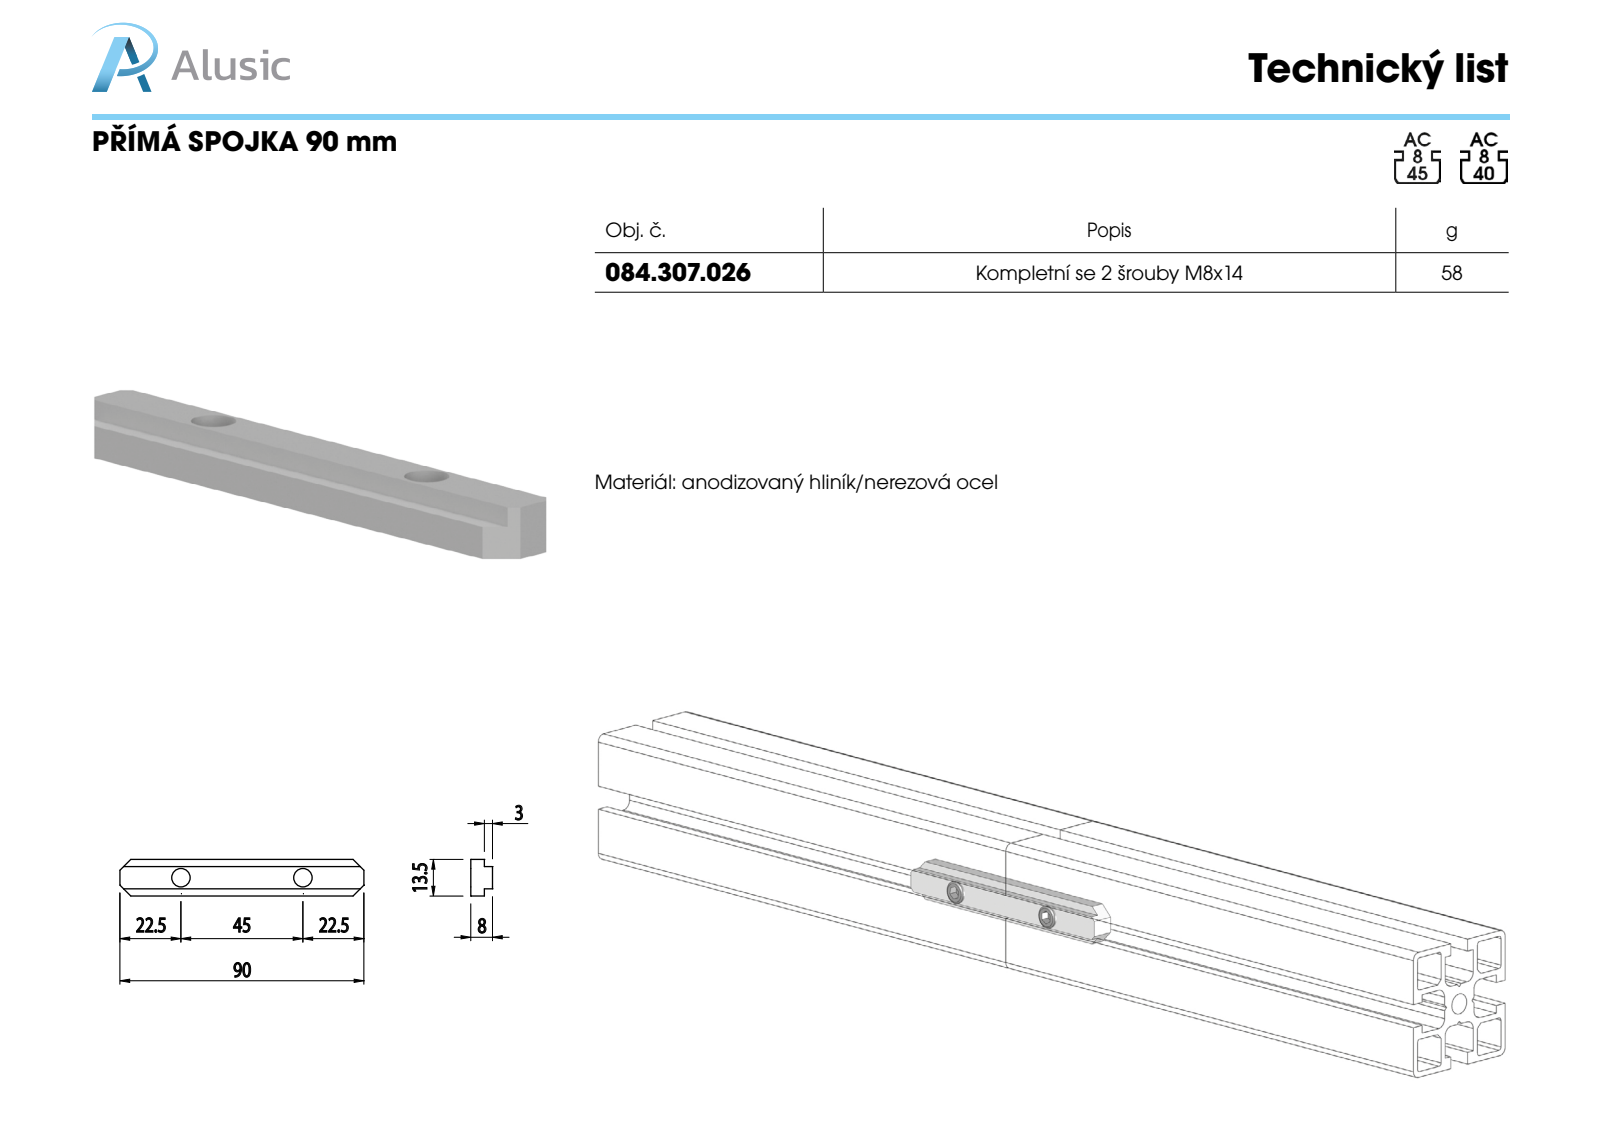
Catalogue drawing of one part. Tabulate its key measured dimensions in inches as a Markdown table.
| quantity | value |
| --- | --- |
| part name | 084.307.026 |
| STEP written by | SolidWorks 2011 (CONFIG_CONTROL_DESIGN) |
| units | inches |
| bodies | 1 solid, 18 faces (14 planar, 4 cylindrical, 0 other) |
| overall size | 3.543 × 0.531 × 0.315 |
| volume | 0.46 in³ |
| surface area | 6.402 in² |
| round holes (diameter × count) | 0.268 × 2 |
| main face-to-face distances | 0.315, 0.104, 0.427, 0.197, 0.118, 0.531, 0.323, 2.658, 3.543 |
| hole center spacings | 1.772 |
